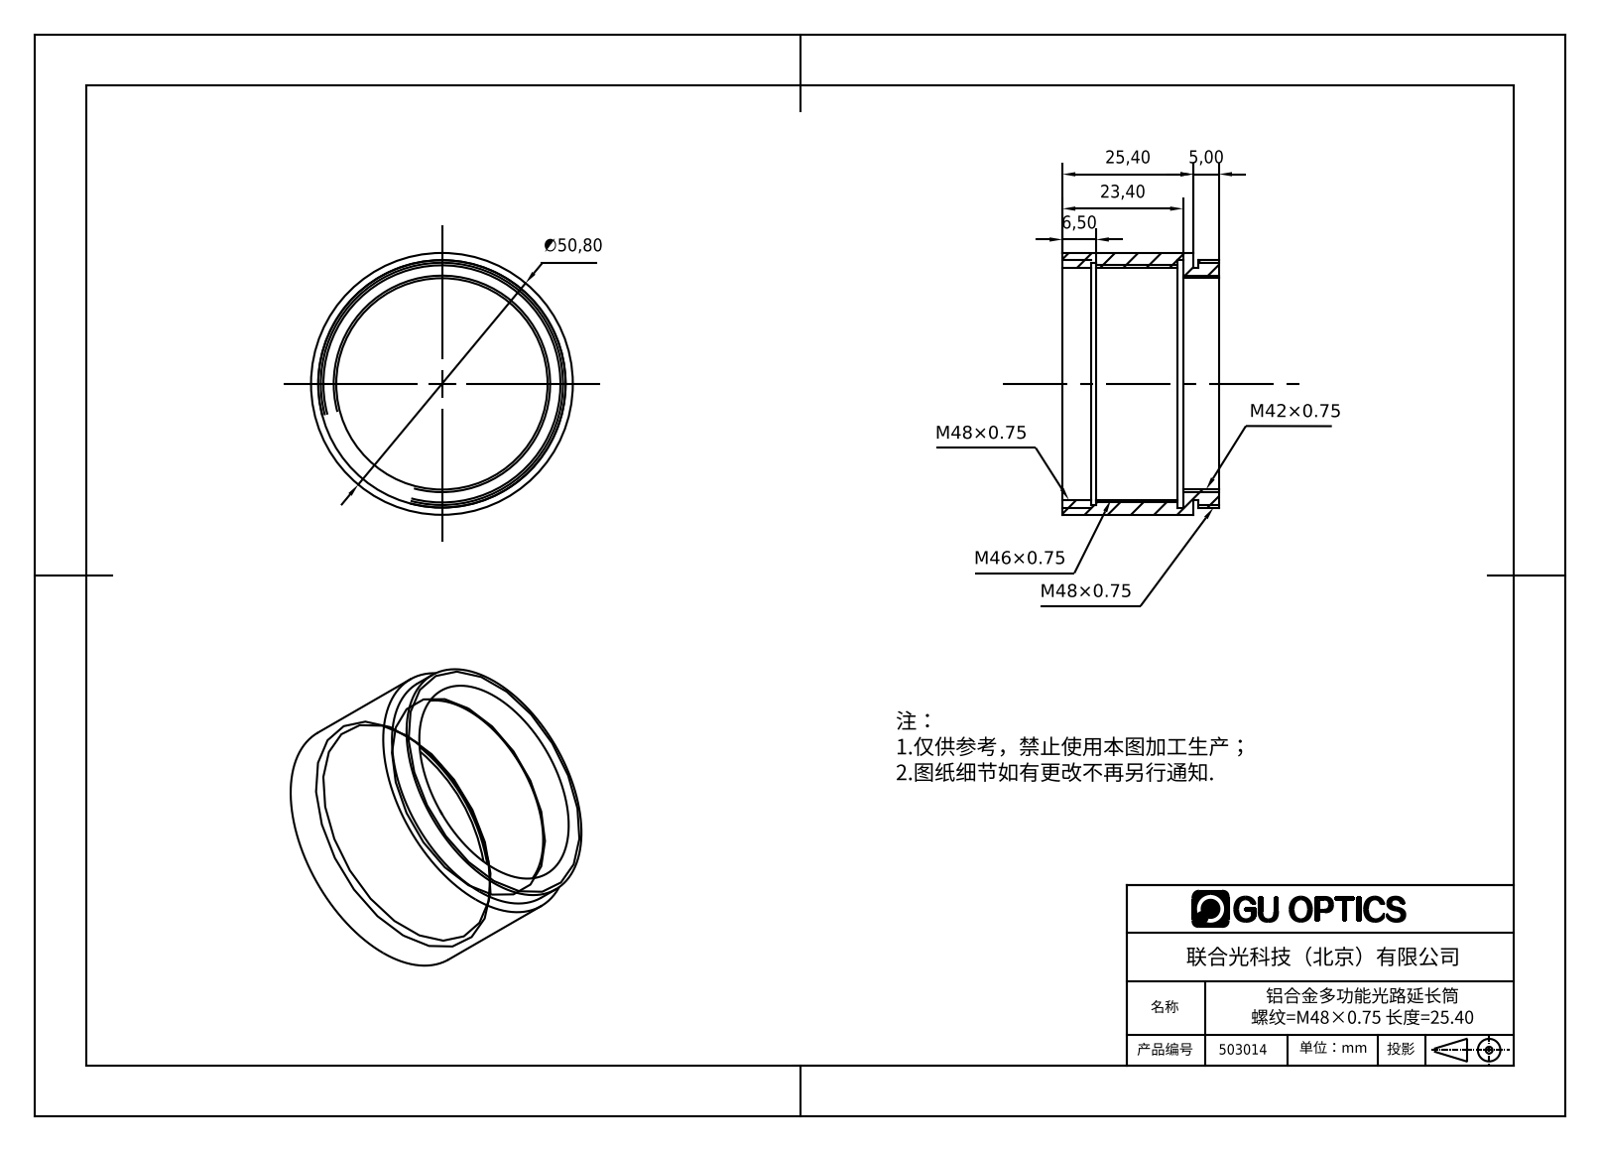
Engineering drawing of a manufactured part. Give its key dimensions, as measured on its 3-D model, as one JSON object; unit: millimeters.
{"part_name": "503014", "step_written_by": "SolidWorks 2016 (AUTOMOTIVE_DESIGN)", "units": "millimeters", "bodies": {"solids": 1, "faces": 24, "planar": 8, "cylindrical": 16, "other": 0}, "overall_size": [50.8, 50.8, 30.4], "volume_mm3": 13489, "surface_area_mm2": 11602, "round_holes": [[41, 1], [45, 1], [47, 1], [48, 1]], "round_bosses_or_shafts": [[50.8, 1]], "face_to_face_distances": [1, 7, 3, 4, 2, 5, 23.4, 25.4, 30.4, 16.9]}
